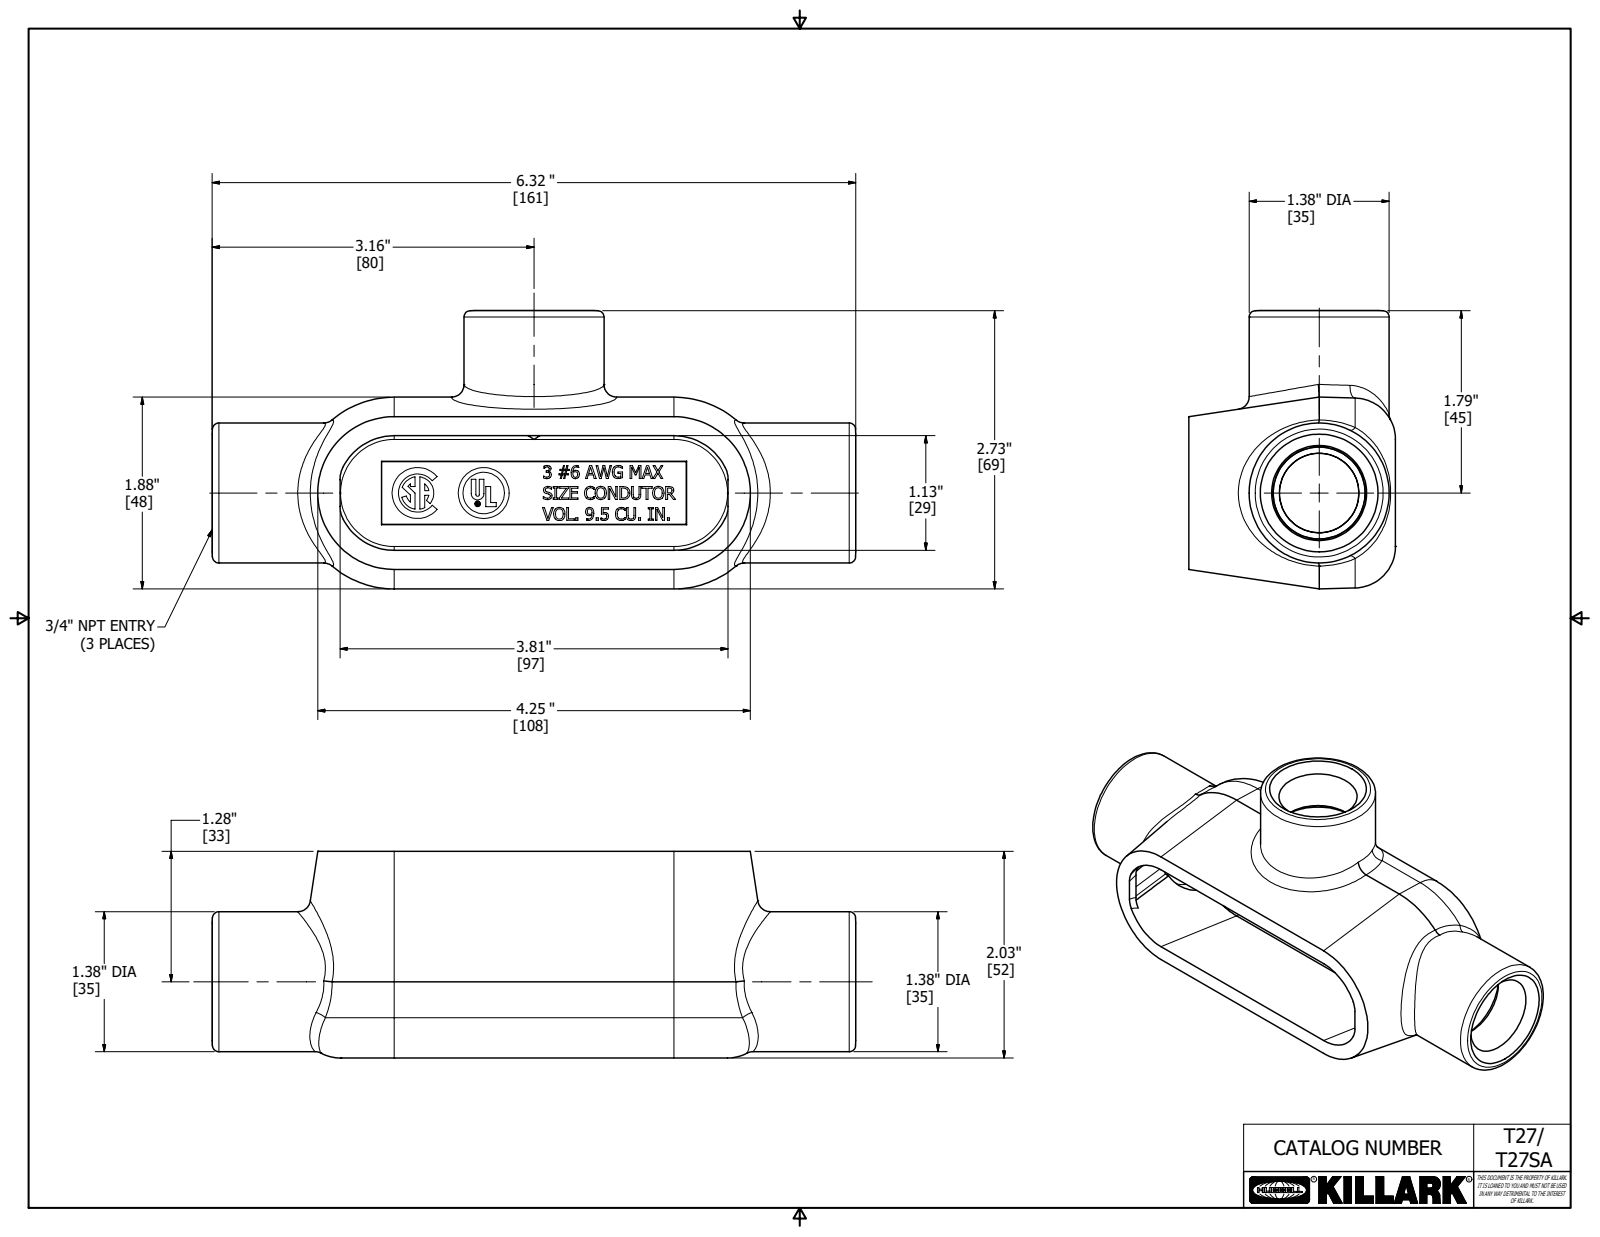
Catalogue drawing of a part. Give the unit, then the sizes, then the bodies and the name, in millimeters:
Units: millimetres
Overall size (bounding box): 160.6 × 69.4 × 51.6
Round holes (diameter × count): ⌀26.8 ×2, ⌀1.2 ×1, ⌀10.3 ×1, ⌀28.6 ×1
Round bosses / shafts (diameter × count): ⌀34.9 ×2, ⌀12.7 ×1, ⌀1.4 ×1
Partial cylindrical surfaces — rounded edges, fillets, slot ends (radius × count): R1.6 ×4, R3.2 ×4, R5.6 ×2, R10.3 ×2, R0.2 ×1, R0.2 ×1, R0.4 ×1, R1.6 ×1
Main face-to-face distances: 4.7, 4.7, 0.8, 51.6, 46.8, 5.6, 46.1, 4, 50.8, 5.6
Hole centre spacings: 3.1
Volume: 107 100 mm³ · Surface area: 47 390 mm²
Bodies: 1 solid, 823 faces (489 planar, 41 cylindrical, 293 other)
Part name (STEP PRODUCT): 17659-2
STEP written by: Autodesk Inventor 2018 (AUTOMOTIVE_DESIGN)
